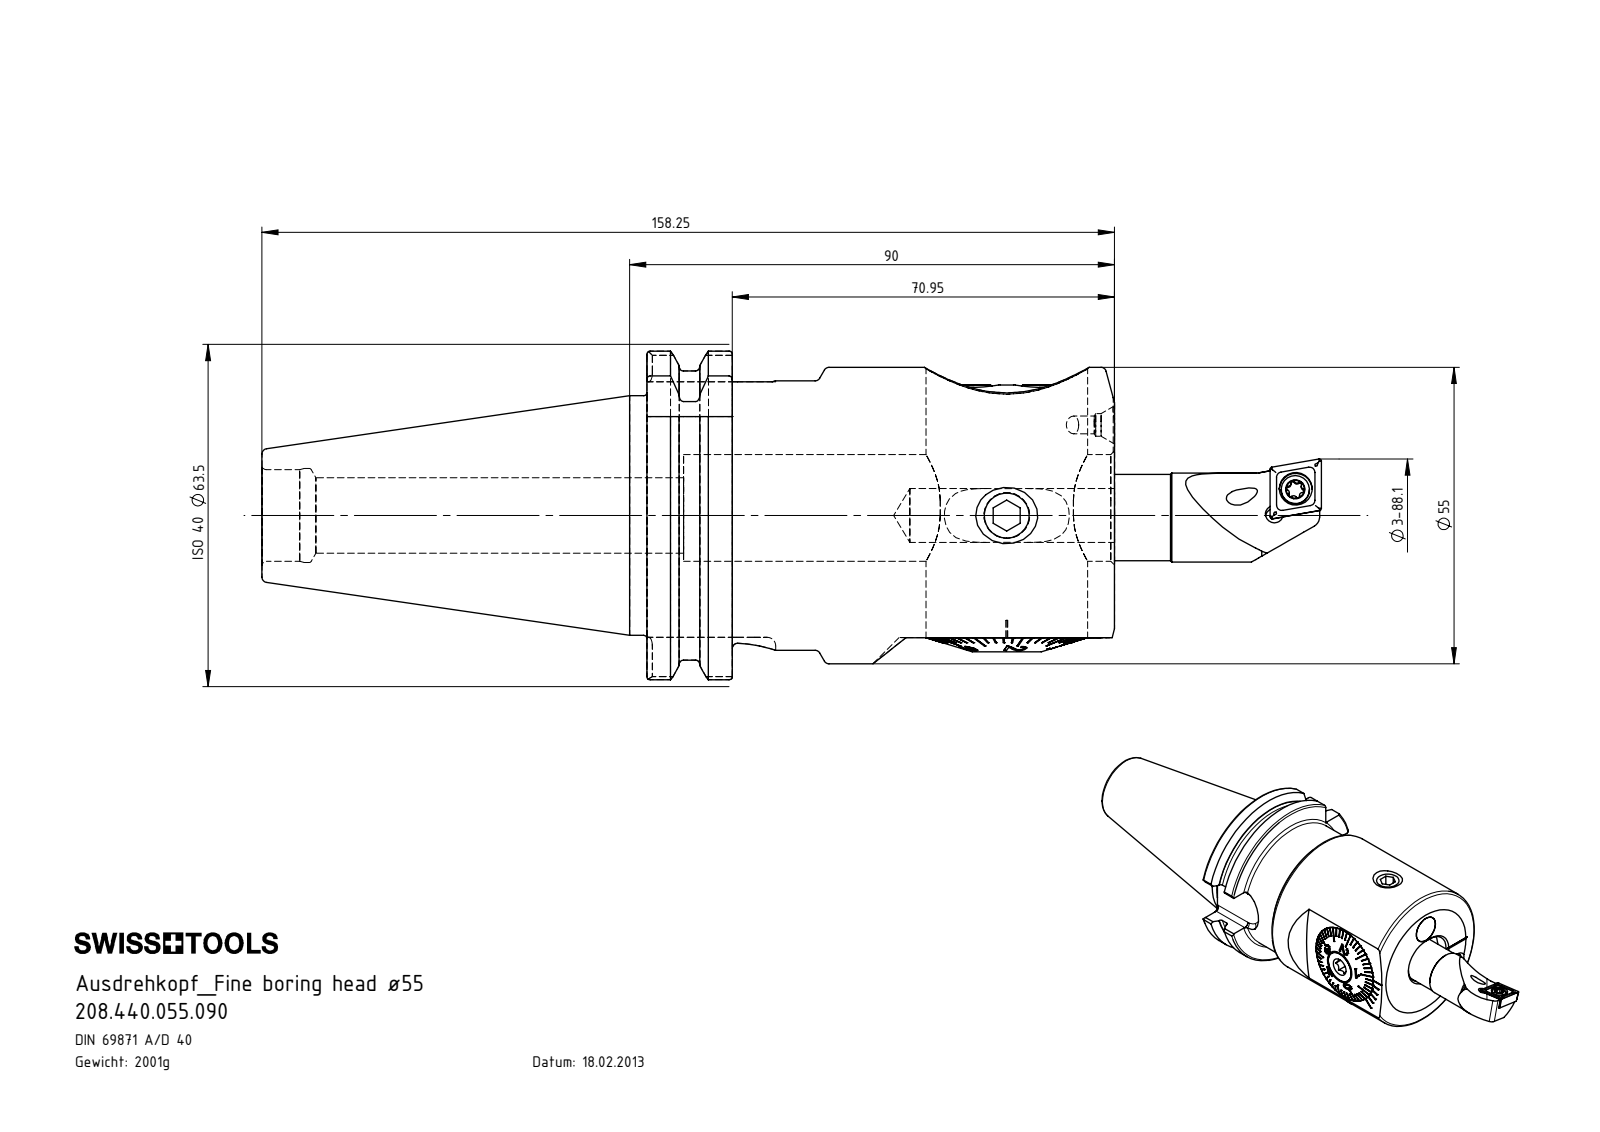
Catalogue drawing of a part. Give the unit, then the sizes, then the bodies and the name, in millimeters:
Units: millimetres
Overall size (bounding box): 158.25 × 63.5 × 60.94
Round holes (diameter × count): ⌀8.5 ×3, ⌀14 ×2, ⌀1 ×1, ⌀1.6 ×1, ⌀2 ×1, ⌀3.3 ×1, ⌀4.2 ×1, ⌀8 ×1, ⌀10 ×1, ⌀11.75 ×1, ⌀12.4 ×1, ⌀14.2 ×1
Round bosses / shafts (diameter × count): ⌀10 ×3, ⌀55 ×1, ⌀50 ×1, ⌀44.45 ×1, ⌀30 ×1, ⌀29.98 ×1, ⌀29.9 ×1, ⌀25 ×1
Partial cylindrical surfaces — rounded edges, fillets, slot ends (radius × count): R1.6 ×8, R0.34 ×6, R0.59 ×6, R3.2 ×3, R0.5 ×1, R3.5 ×1, R8 ×1, R8.05 ×1
Main face-to-face distances: 86.8, 15.85, 70.95, 5.3, 6.48, 1.18, 3.68, 2.8, 2.5, 5
Hole centre spacings: 14.5, 7.25, 0.37, 14.7, 15.07, 18.83, 19.16, 20.91
Volume: 235 728 mm³ · Surface area: 56 537 mm²
Bodies: 16 solids, 809 faces (345 planar, 153 cylindrical, 311 other)
Part name (STEP PRODUCT): A55-BG2.011.016_E; A55-BG3.011.033_A_PreviewCfg; WCB-ER2.001.009_A; A55-BG2.012.006_B (+8 more)
STEP written by: SolidWorks 2017 (AUTOMOTIVE_DESIGN)
